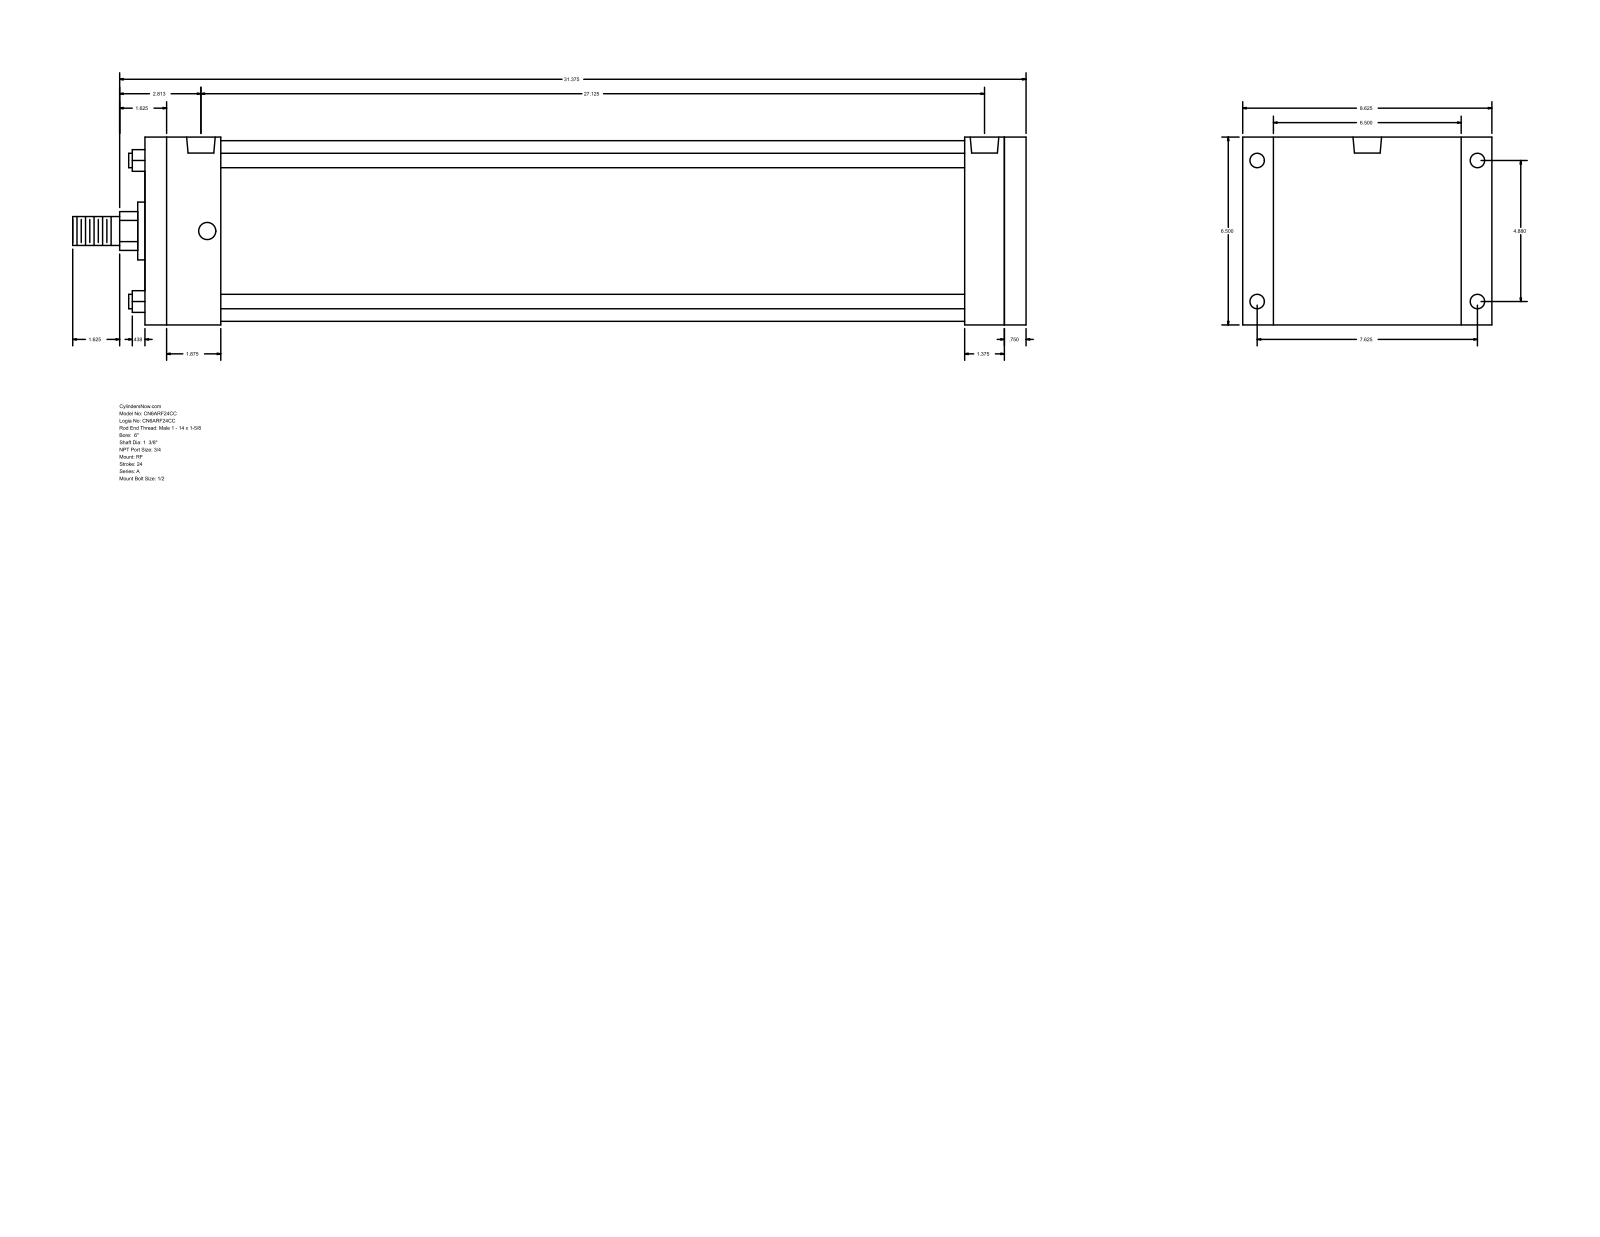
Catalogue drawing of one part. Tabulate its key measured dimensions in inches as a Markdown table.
| quantity | value |
| --- | --- |
| part name | A_RF__0600_1.375 |
| STEP written by | GSSL Pune (CONFIG_CONTROL_DESIGN) |
| units | inches |
| bodies | 0 solids, 92 faces (64 planar, 28 cylindrical, 0 other) |
| overall size | 33 × 8.625 × 6.5 |
| round holes (diameter × count) | 0.5 × 4, 0.594 × 4, 0.989 × 2 |
| round bosses / shafts (diameter × count) | 0.5 × 4, 6.25 × 1, 2 × 1, 1.375 × 1, 1 × 1 |
| partial cylindrical surfaces (radius × count) | 0.672 × 1 |
| main face-to-face distances | 6.5, 30.5, 29.75, 0.75, 2.125, 2.625, 27.125, 27.875, 28.375, 25.75 |
| hole center spacings | 0.219, 4.88, 7.625, 9.053, 26.687, 26.906, 27.125 |
